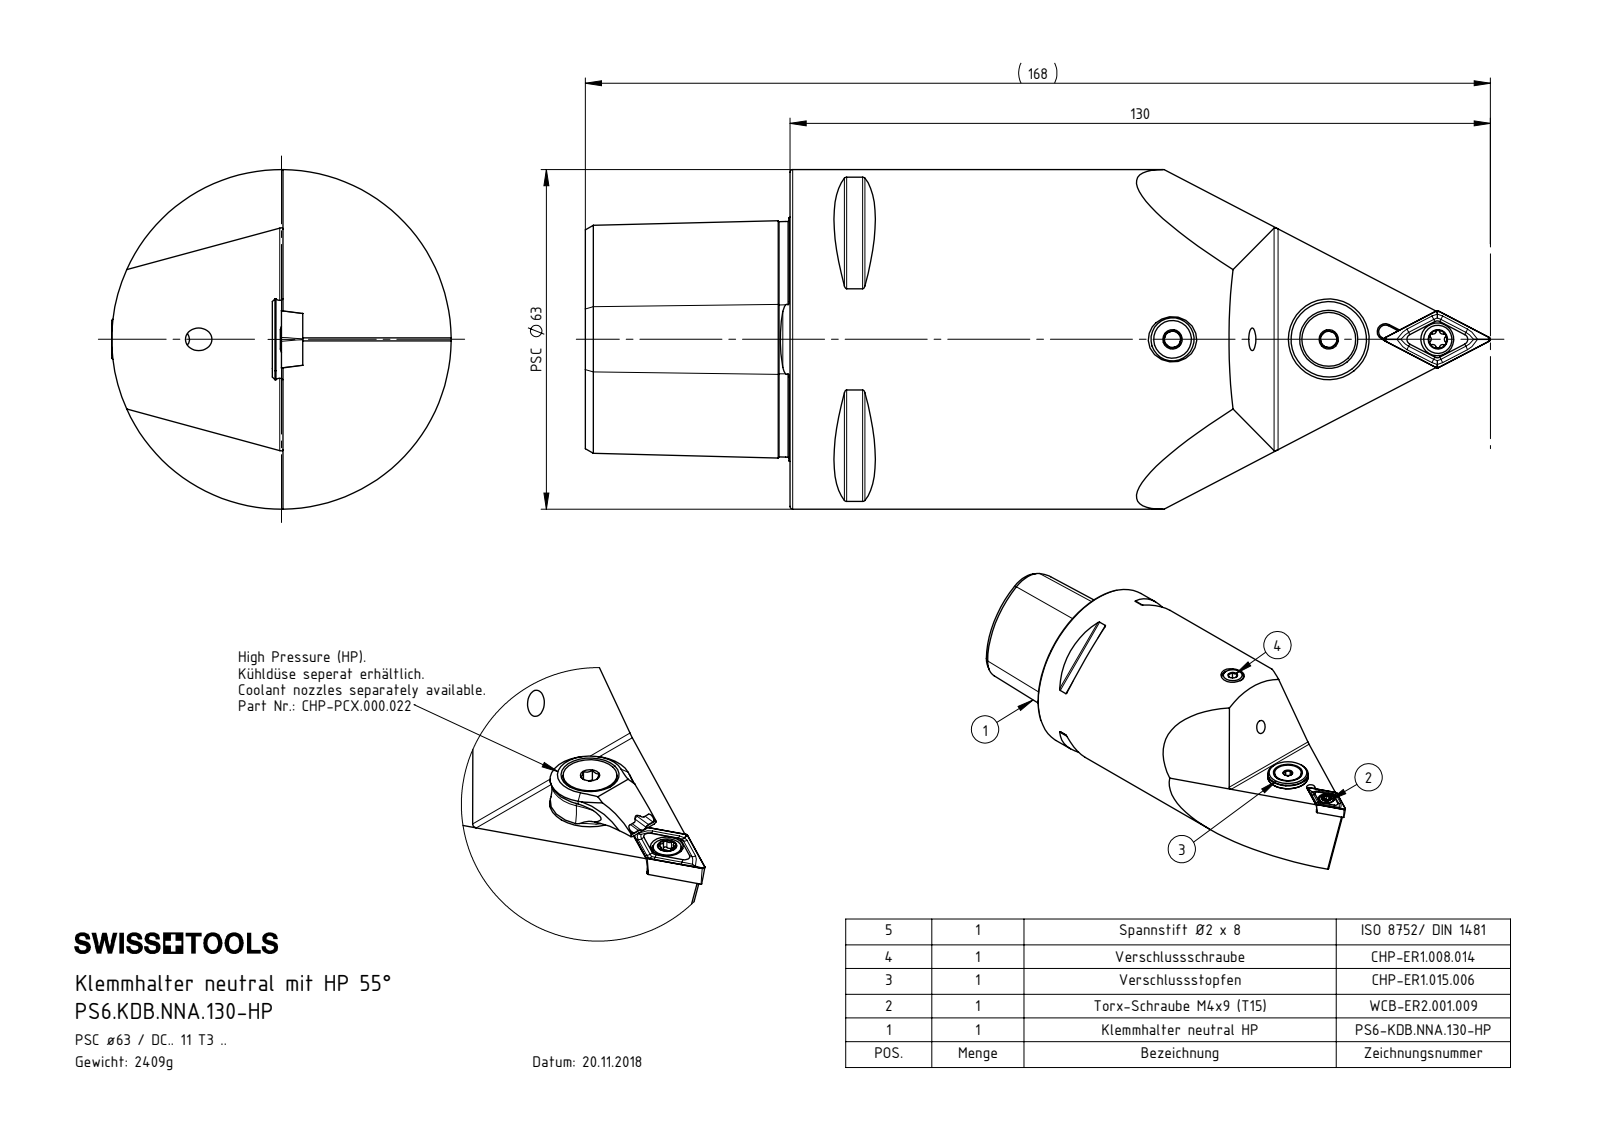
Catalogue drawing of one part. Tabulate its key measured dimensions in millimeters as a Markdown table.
| quantity | value |
| --- | --- |
| part name | CHP-ER1.015.006_A; DCMT11T304; PS6-KDB.NNA.130-HP_A; DIN 7991 - M5x15 (+6 more) |
| STEP written by | SolidWorks 2017 (AUTOMOTIVE_DESIGN) |
| units | millimeters |
| bodies | 8 solids, 267 faces (89 planar, 59 cylindrical, 119 other) |
| overall size | 168.01 × 63.13 × 63 |
| volume | 306 416 mm³ |
| surface area | 41 046 mm² |
| round holes (diameter × count) | 4.2 × 3, 1.2 × 1, 2 × 1, 2.5 × 1, 3 × 1, 3.3 × 1, 4 × 1, 4.4 × 1, 5 × 1, 5.2 × 1, 6.1 × 1, 7 × 1 |
| round bosses / shafts (diameter × count) | 63 × 1, 15 × 1, 13.4 × 1, 10 × 1, 8 × 1, 5.5 × 1, 5.25 × 1, 5 × 1 |
| partial cylindrical surfaces (radius × count) | 0.5 × 10, 0.34 × 6, 0.59 × 6, 1.25 × 1, 6 × 1, 7 × 1 |
| main face-to-face distances | 85, 38, 123, 24.88, 4.5, 27, 11, 96, 55.8, 0.83 |
| hole center spacings | 4.5, 16.82, 16.92, 20.19, 20.29, 27.5, 88.09, 91.37 |
